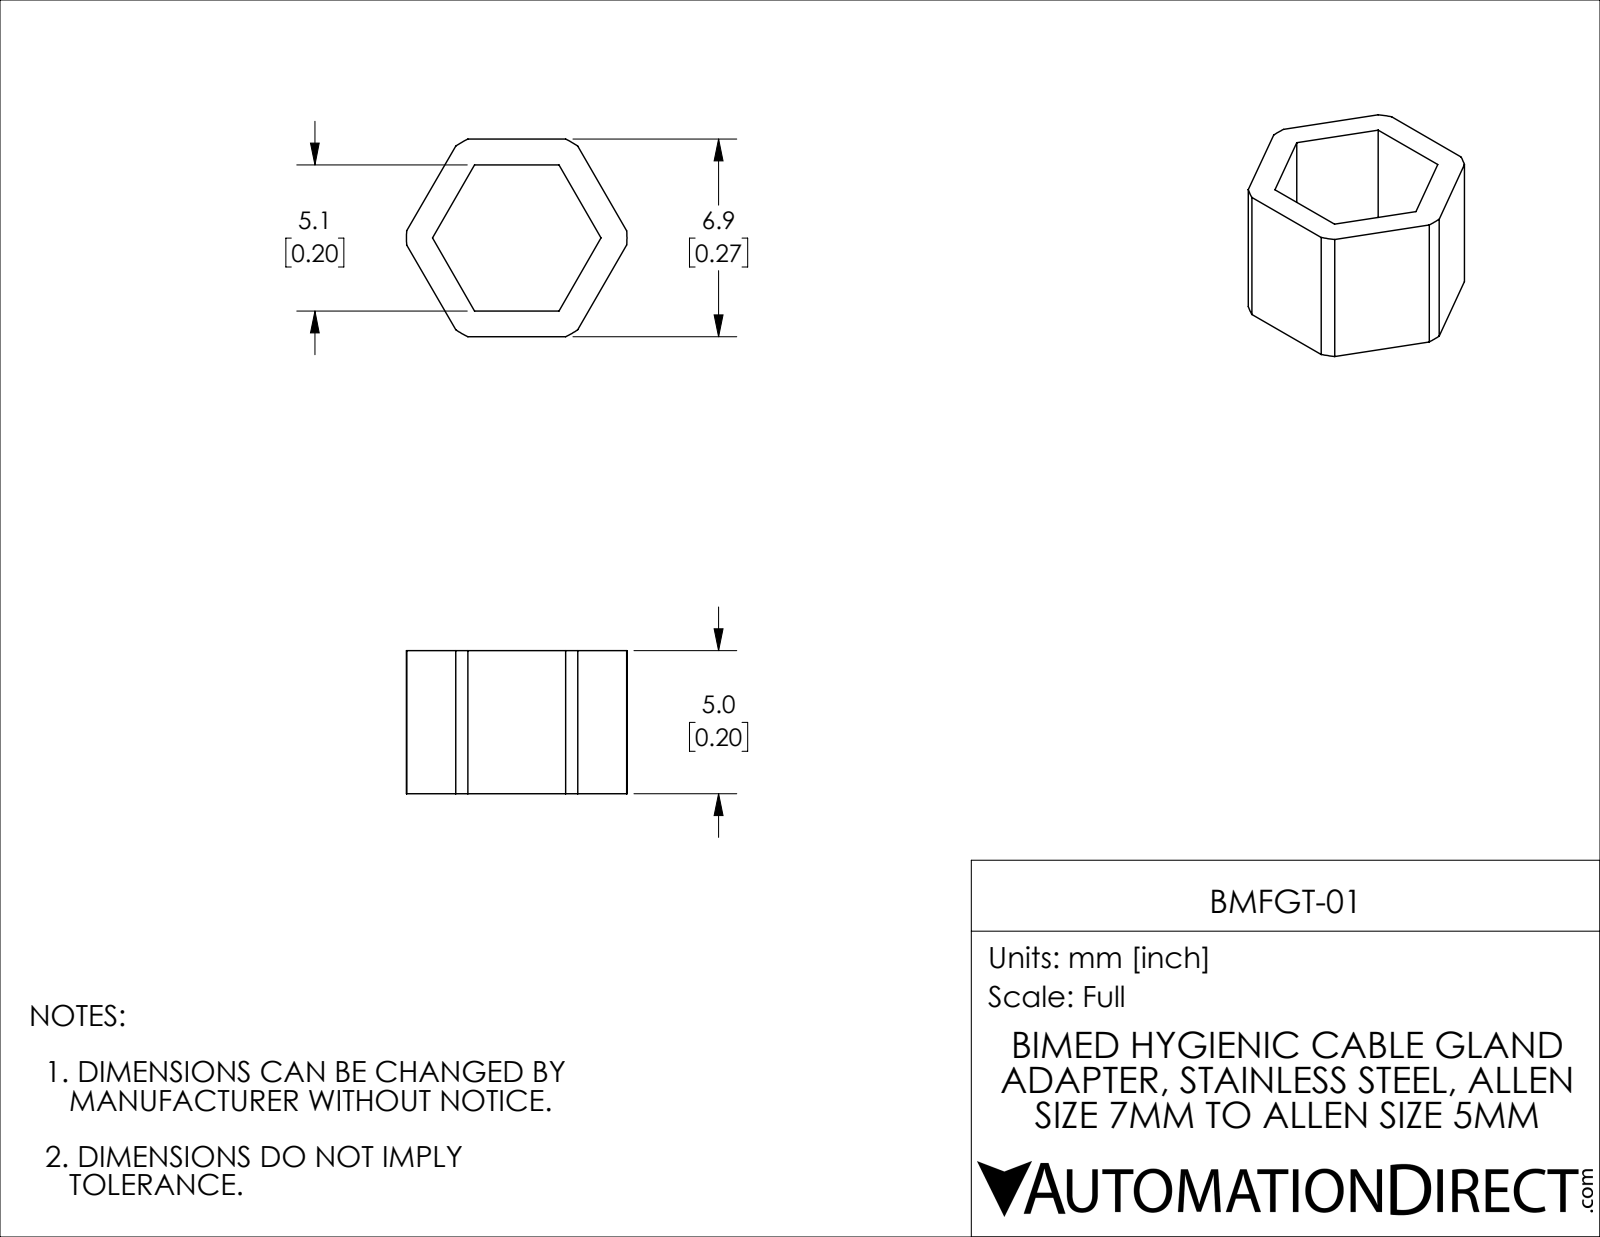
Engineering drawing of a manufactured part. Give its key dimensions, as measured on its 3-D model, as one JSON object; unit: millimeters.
{"part_name": "BMFGT-01", "step_written_by": "SolidWorks 2021 (CONFIG_CONTROL_DESIGN)", "units": "millimeters", "bodies": {"solids": 1, "faces": 20, "planar": 14, "cylindrical": 6, "other": 0}, "overall_size": [7.7, 6.9, 5], "volume_mm3": 93, "surface_area_mm2": 243, "partial_cylinders_radius": [[3.85, 1]], "face_to_face_distances": [0.9, 6, 6.9, 5.1, 5]}
